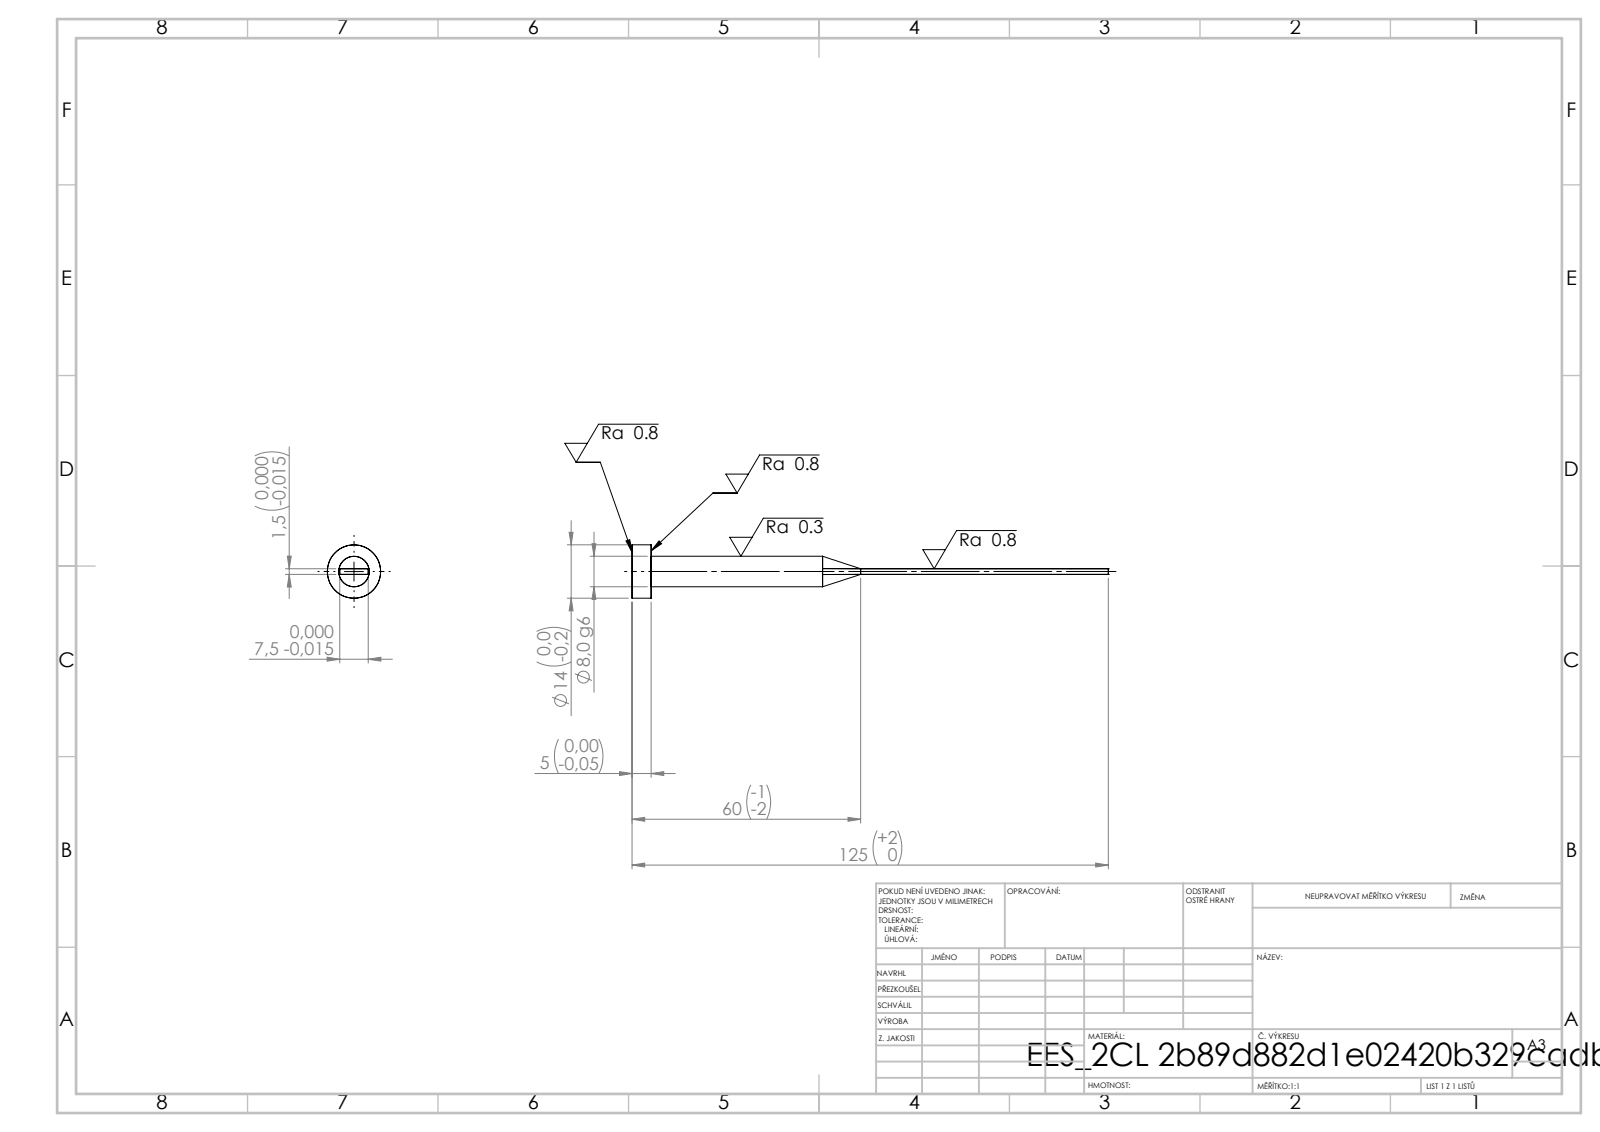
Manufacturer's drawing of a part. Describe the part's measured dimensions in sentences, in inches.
Its 3-D file was written by "SolidWorks 2019 (CONFIG_CONTROL_DESIGN)". It is 1 solid with 15 faces: 7 planar, 4 cylindrical and 4 other. Overall it measures 4.921 by 0.551 by 0.551 inches. Its volume is 0.247 cubic inches and its surface area 4.652 square inches. Round bosses or shafts: 1 of diameter 0.551, 1 of diameter 0.315. The main face-to-face distances are 0.059, 0.197, 0.295, 4.921, 4.724.
